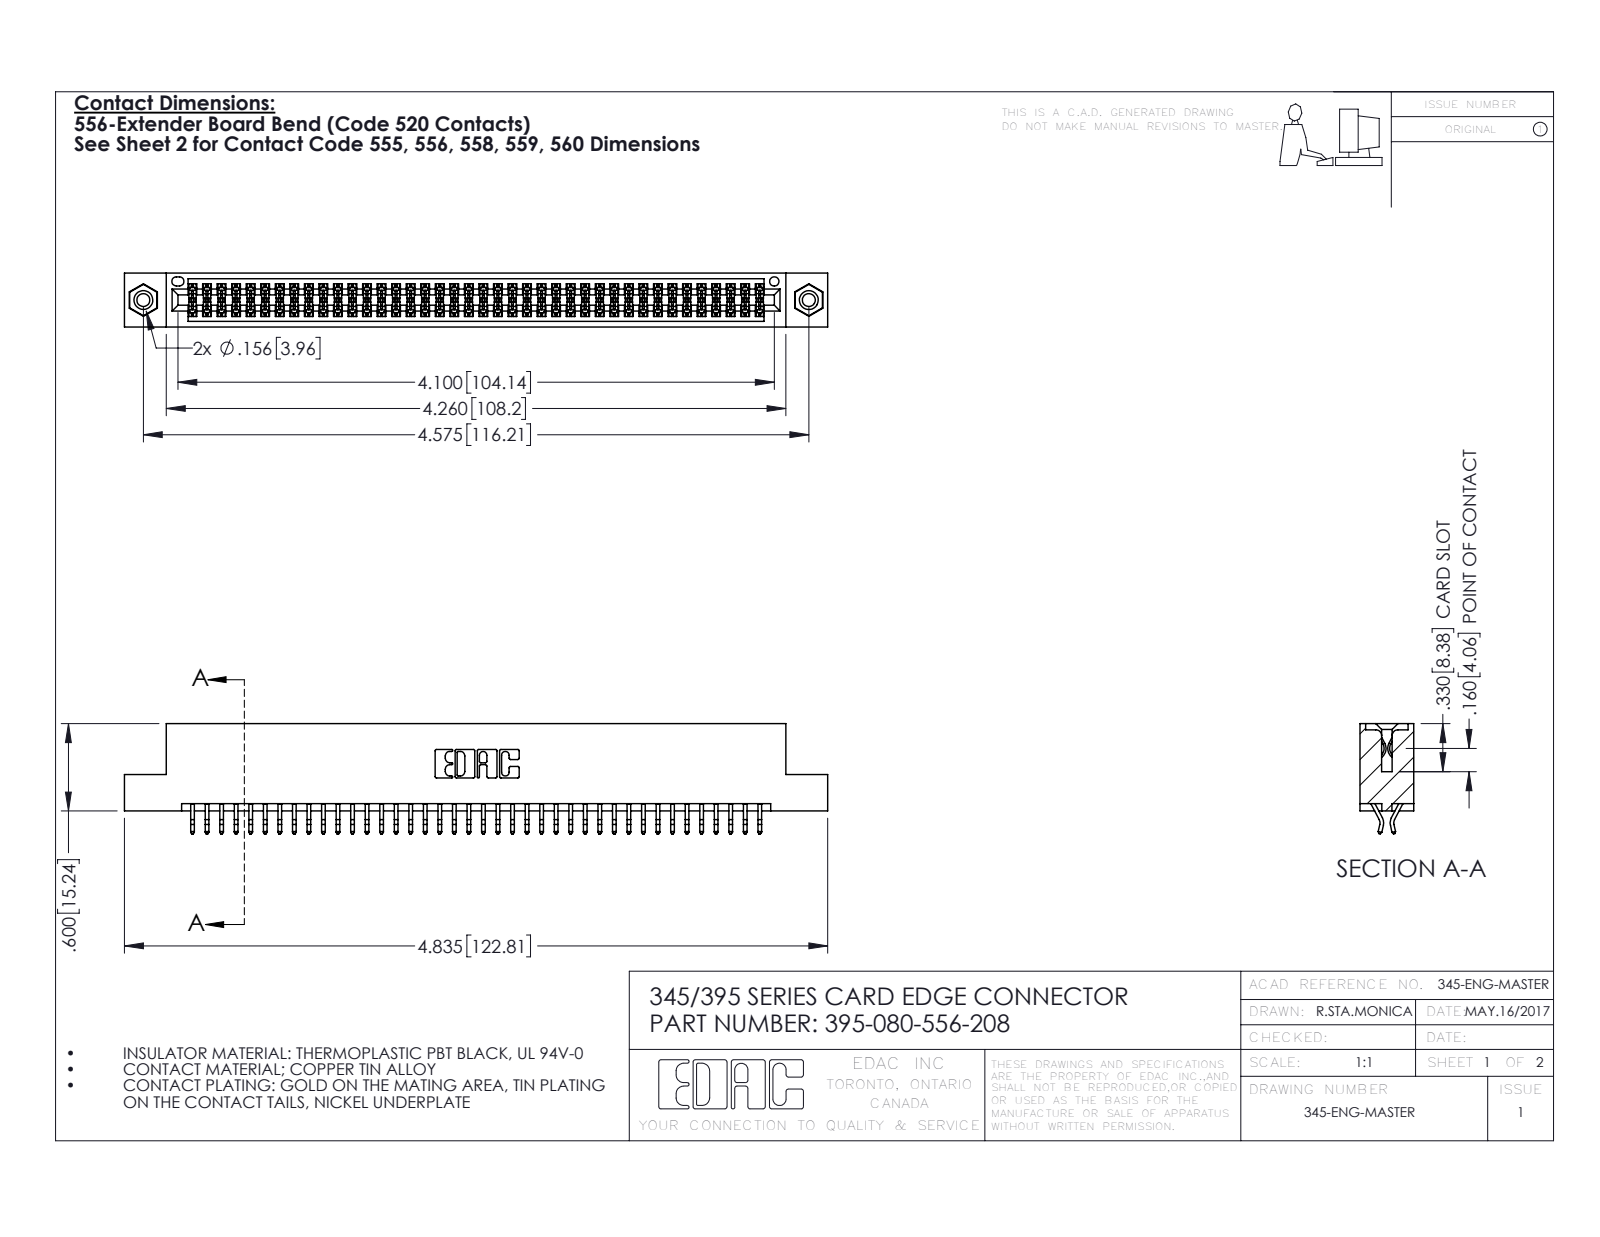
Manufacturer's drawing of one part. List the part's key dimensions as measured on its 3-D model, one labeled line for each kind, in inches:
Part name (STEP PRODUCT): 345-292-001_556 Tail; 395-080-556-208; 345-250-001_345-250-003-102; 345 Part_Flush Mounting Lugs - 0.156 Dia-TI
STEP written by: SolidWorks 2016 (CONFIG_CONTROL_DESIGN)
Units: inches
Bodies: 83 solids, 4666 faces (3072 planar, 1578 cylindrical, 16 other)
Overall size (bounding box): 4.835 × 0.757 × 0.37
Volume: 0.726 in³ · Surface area: 27.12 in²
Round holes (diameter × count): ⌀0.089 ×2, ⌀0.125 ×2, ⌀0.156 ×2, ⌀0.064 ×1
Round bosses / shafts (diameter × count): ⌀0.155 ×2
Partial cylindrical surfaces — rounded edges, fillets, slot ends (radius × count): R0.006 ×120, R0.01 ×22, R0.007 ×6, R0.031 ×6, R0.026 ×3, R0.01 ×2, R0.014 ×2, R0.019 ×2
Main face-to-face distances: 0.072, 0.298, 0.37, 0.2, 0.025, 0.098, 0.272, 0.225, 0.175, 0.149
Hole centre spacings: 0.27, 4.339, 4.575
